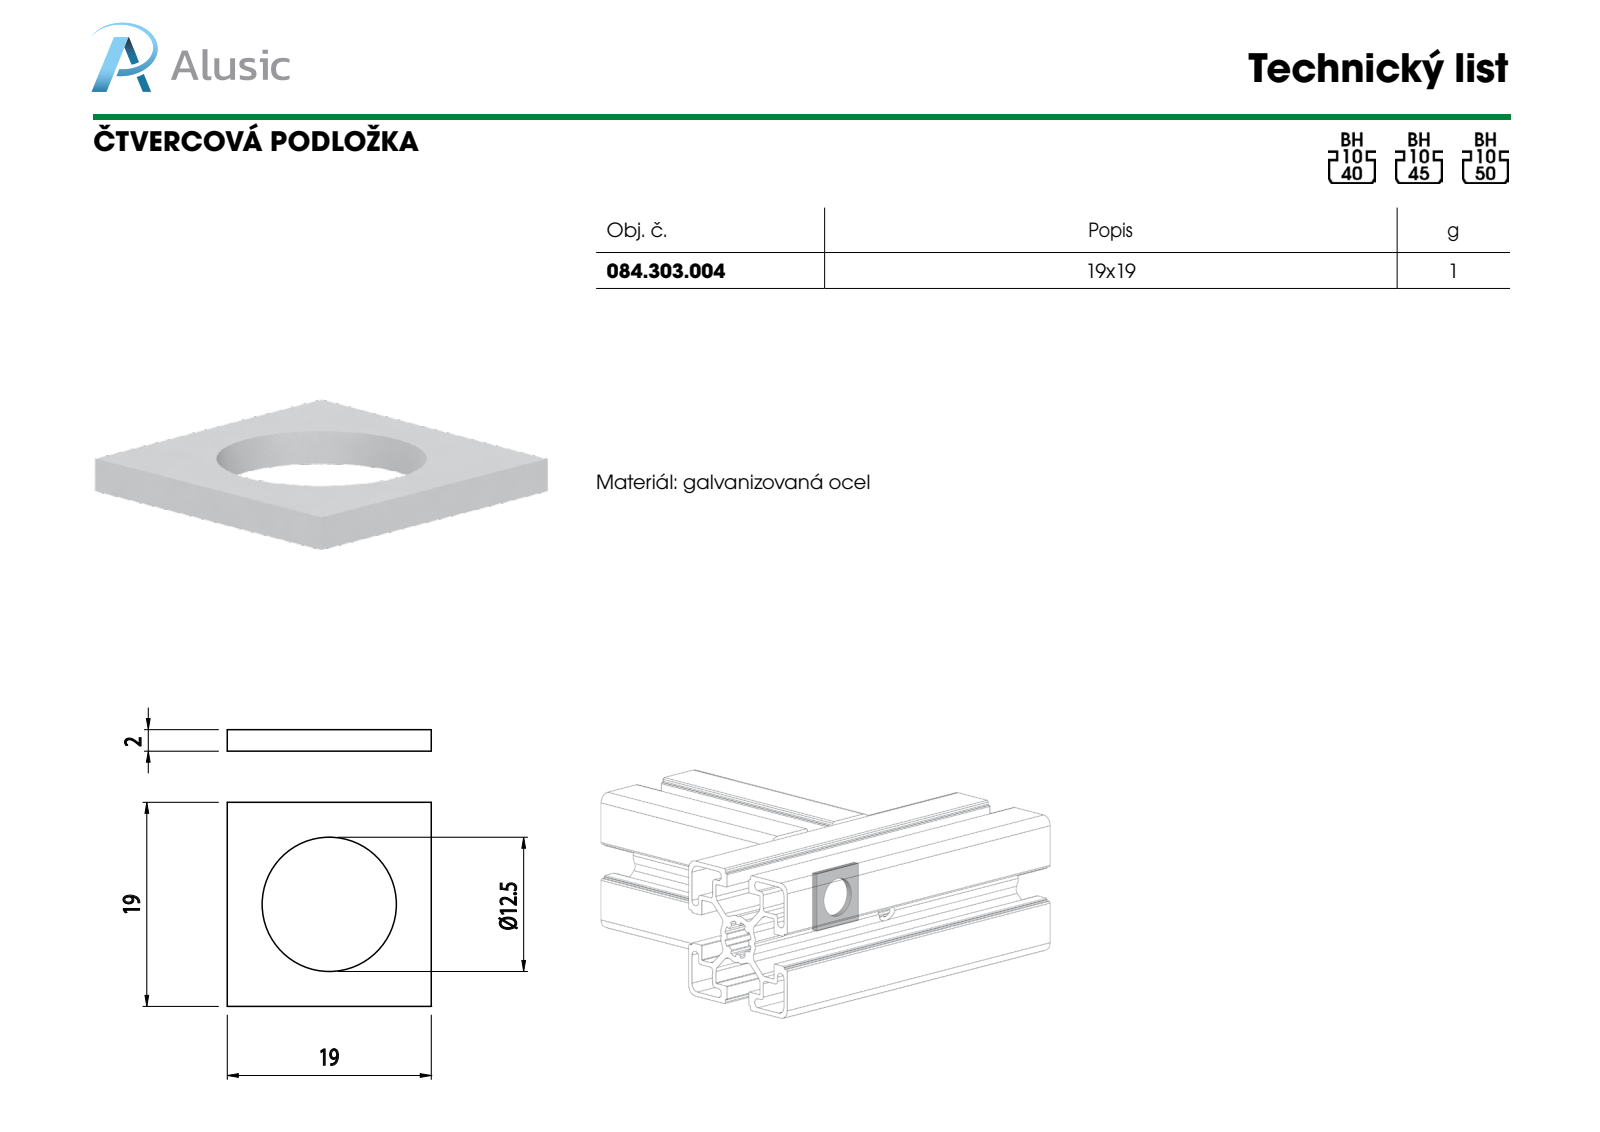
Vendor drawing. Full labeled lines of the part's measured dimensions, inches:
Part name (STEP PRODUCT): 084.303.004
STEP written by: SolidWorks 2011 (CONFIG_CONTROL_DESIGN)
Units: inches
Bodies: 1 solid, 8 faces (6 planar, 2 cylindrical, 0 other)
Overall size (bounding box): 0.748 × 0.748 × 0.079
Volume: 0.029 in³ · Surface area: 1.1 in²
Round holes (diameter × count): ⌀0.492 ×1
Main face-to-face distances: 0.079, 0.748
